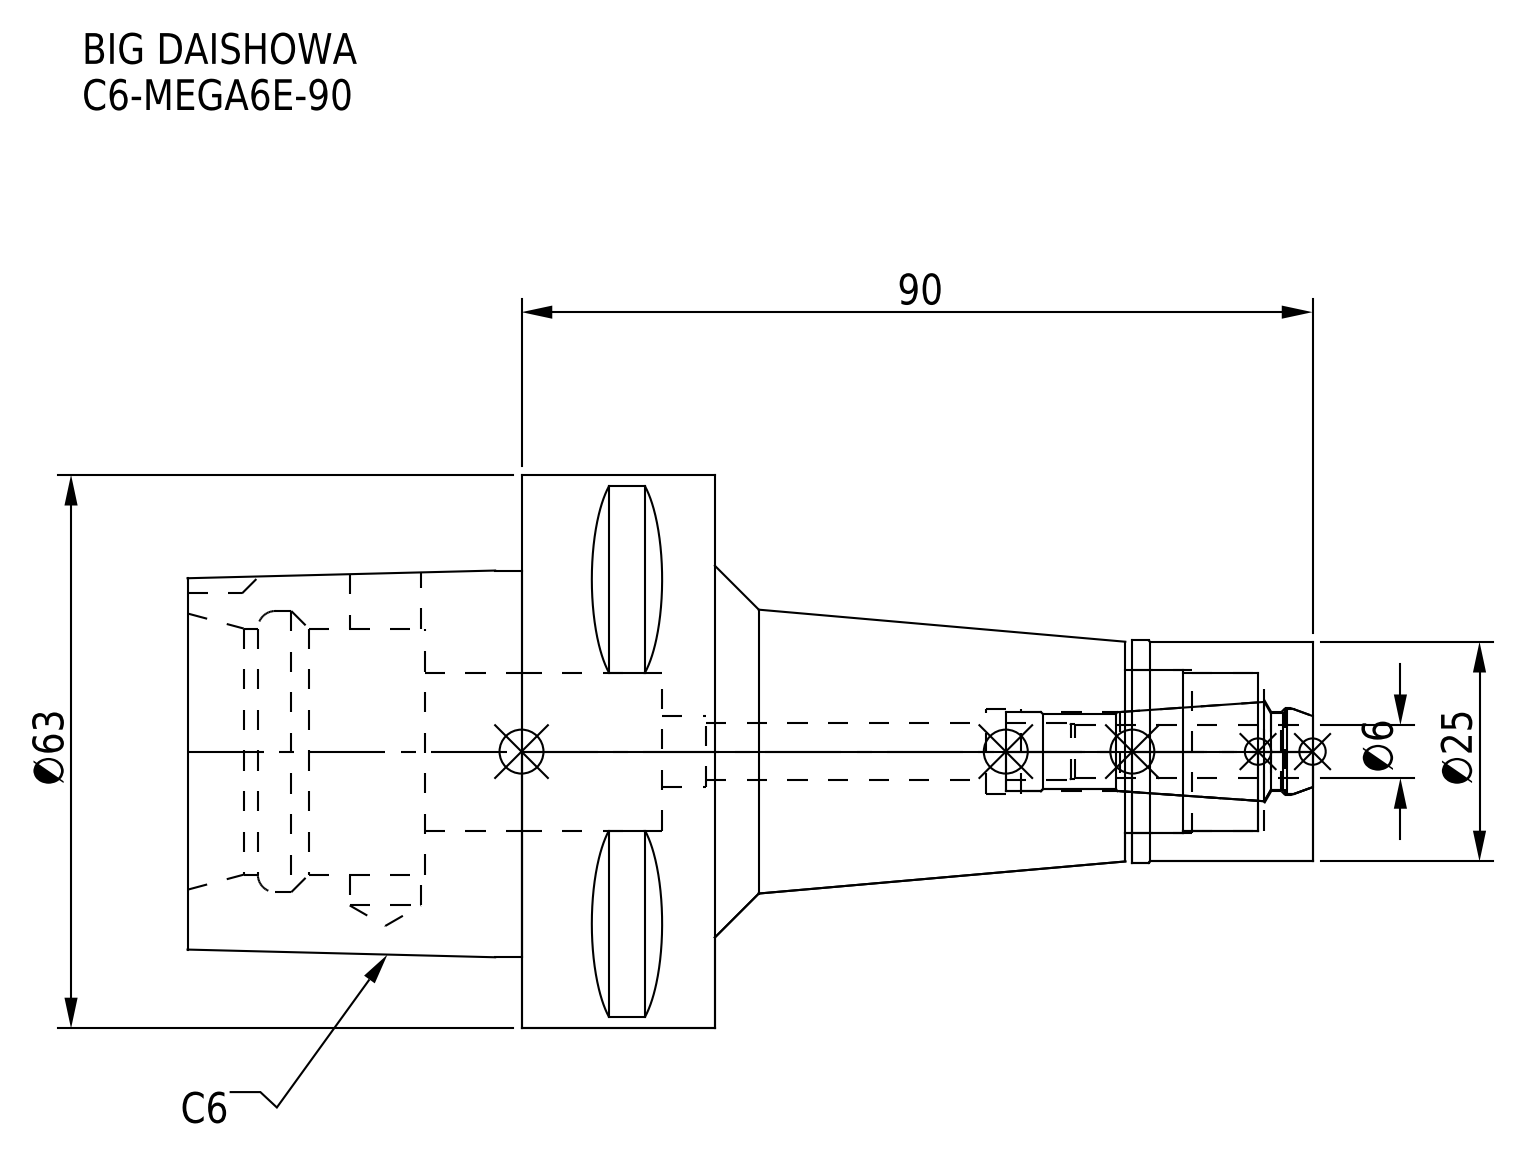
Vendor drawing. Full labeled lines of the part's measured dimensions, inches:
Part name (STEP PRODUCT): DXF_TEMP_ASSY_ASM_4_ASM.stp; C6-MEGA6E-90-060.stp; MEN6_1.stp; C6-MEGA6E-90-060-FreeParts (+3 more)
STEP written by: SolidWorks 2019 (CONFIG_CONTROL_DESIGN)
Units: inches
Bodies: 2 solids, 100 faces (37 planar, 39 cylindrical, 24 other)
Overall size (bounding box): 5.039 × 2.48 × 2.48
Volume: 8.256 in³ · Surface area: 46.22 in²
Round holes (diameter × count): ⌀0.252 ×1, ⌀0.315 ×1, ⌀0.319 ×1, ⌀0.354 ×1, ⌀0.378 ×1, ⌀0.39 ×1, ⌀0.709 ×1, ⌀0.728 ×1, ⌀1.102 ×1, ⌀1.26 ×1
Round bosses / shafts (diameter × count): ⌀2.48 ×1, ⌀0.996 ×1, ⌀0.984 ×1
Partial cylindrical surfaces — rounded edges, fillets, slot ends (radius × count): R0.197 ×1
Main face-to-face distances: 0.866, 1.063, 2.362, 1.496, 2.677, 3.543, 5.039, 3.976, 1.299, 0.433
